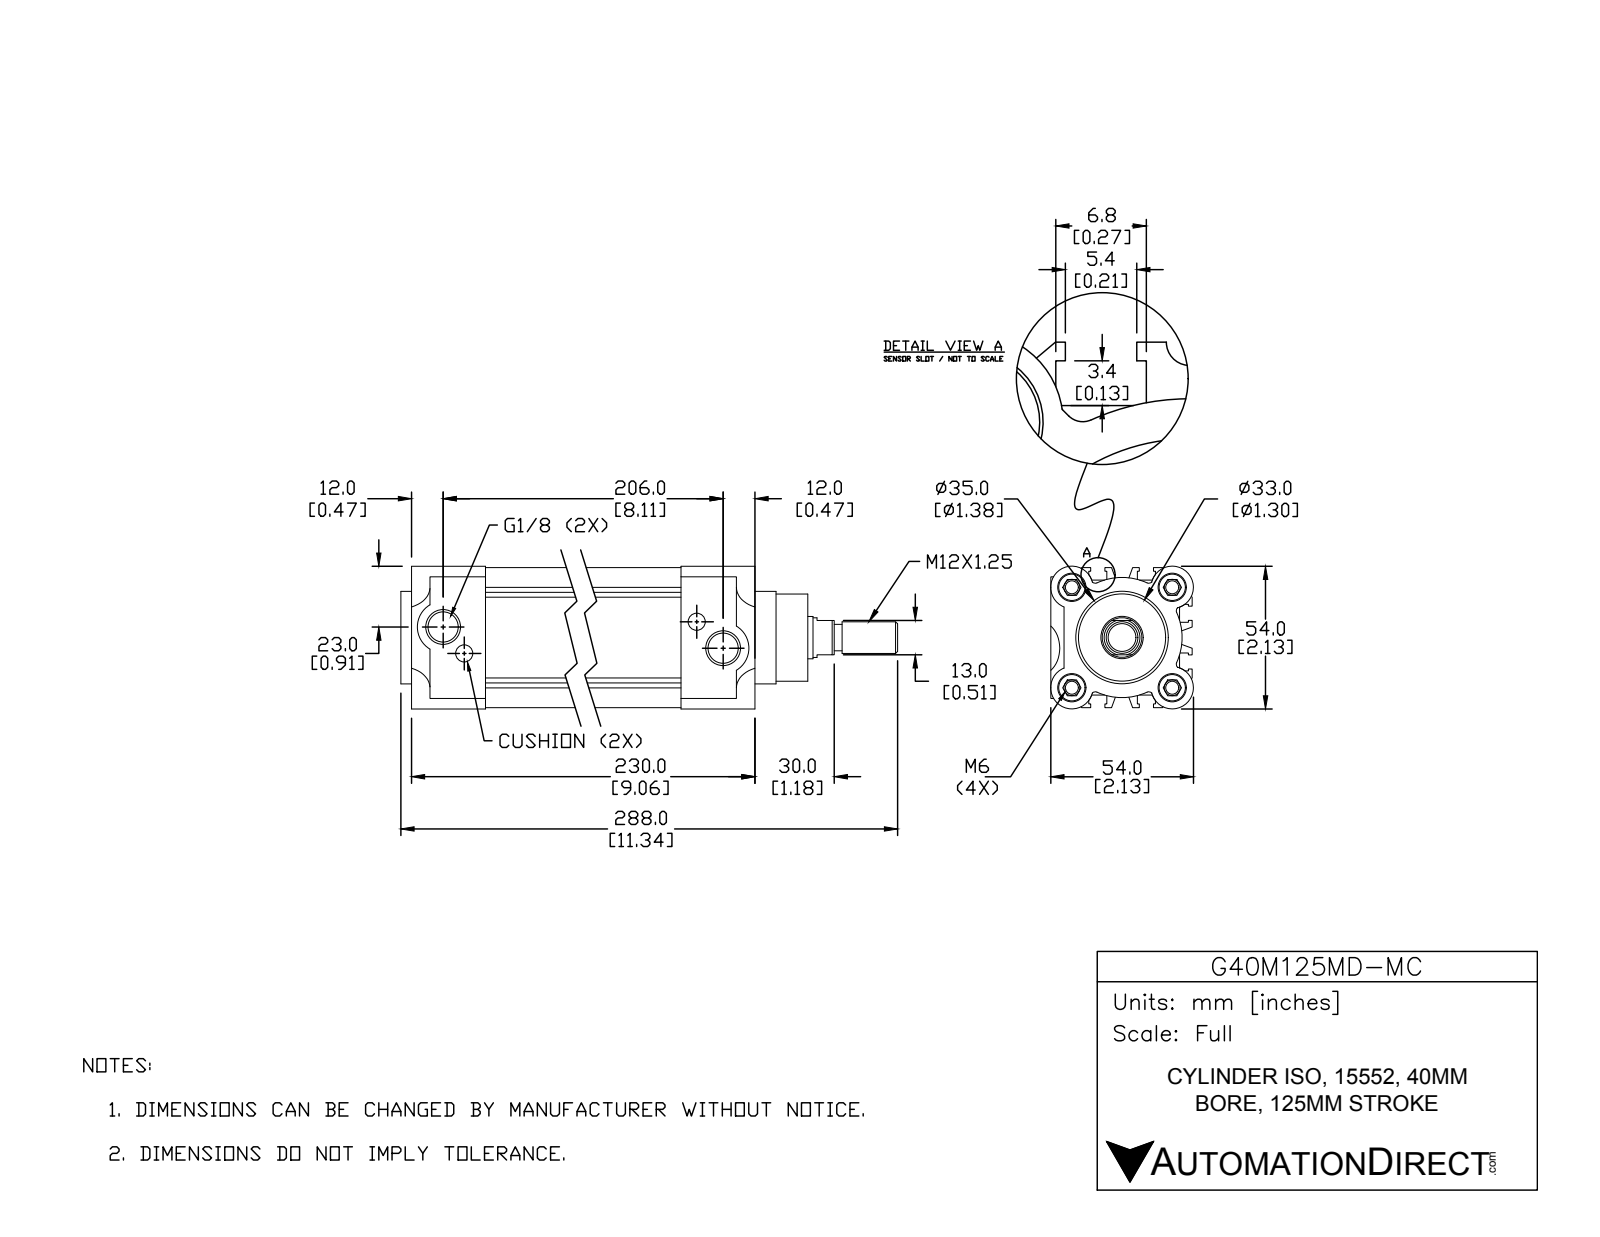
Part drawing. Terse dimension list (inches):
name: 40-125-83-B; G40M125MD-MC; 40121125-R; 40121-HR (+1 more)
written by: SolidWorks 2015 (CONFIG_CONTROL_DESIGN)
unit: in
bodies: 4 solids, 418 faces (236 planar, 138 cylindrical, 44 other)
size: 11.339 × 2.126 × 2.126
volume: 27.65 in³; area: 211.3 in²
holes: 4× ⌀0.194, 4× ⌀0.421, 2× ⌀0.256, 2× ⌀0.451, 1× ⌀0.63
bosses: 5× ⌀0.394, 1× ⌀1.575, 1× ⌀1.378, 1× ⌀1.299, 1× ⌀0.591, 1× ⌀0.472
rounds: 12× R0.059, 6× R0.004, 4× R0.295, 4× R0.315, 2× R0.384, 1× R0.886, 1× R0.896
face distances: 1.9, 0.187, 2.087, 0.724, 0.954, 1.372, 0.547, 1.539, 0.815, 1.272
hole spacings: 1.058, 1.496, 2.116, 0.504, 0.557, 7.417, 7.717, 7.796
